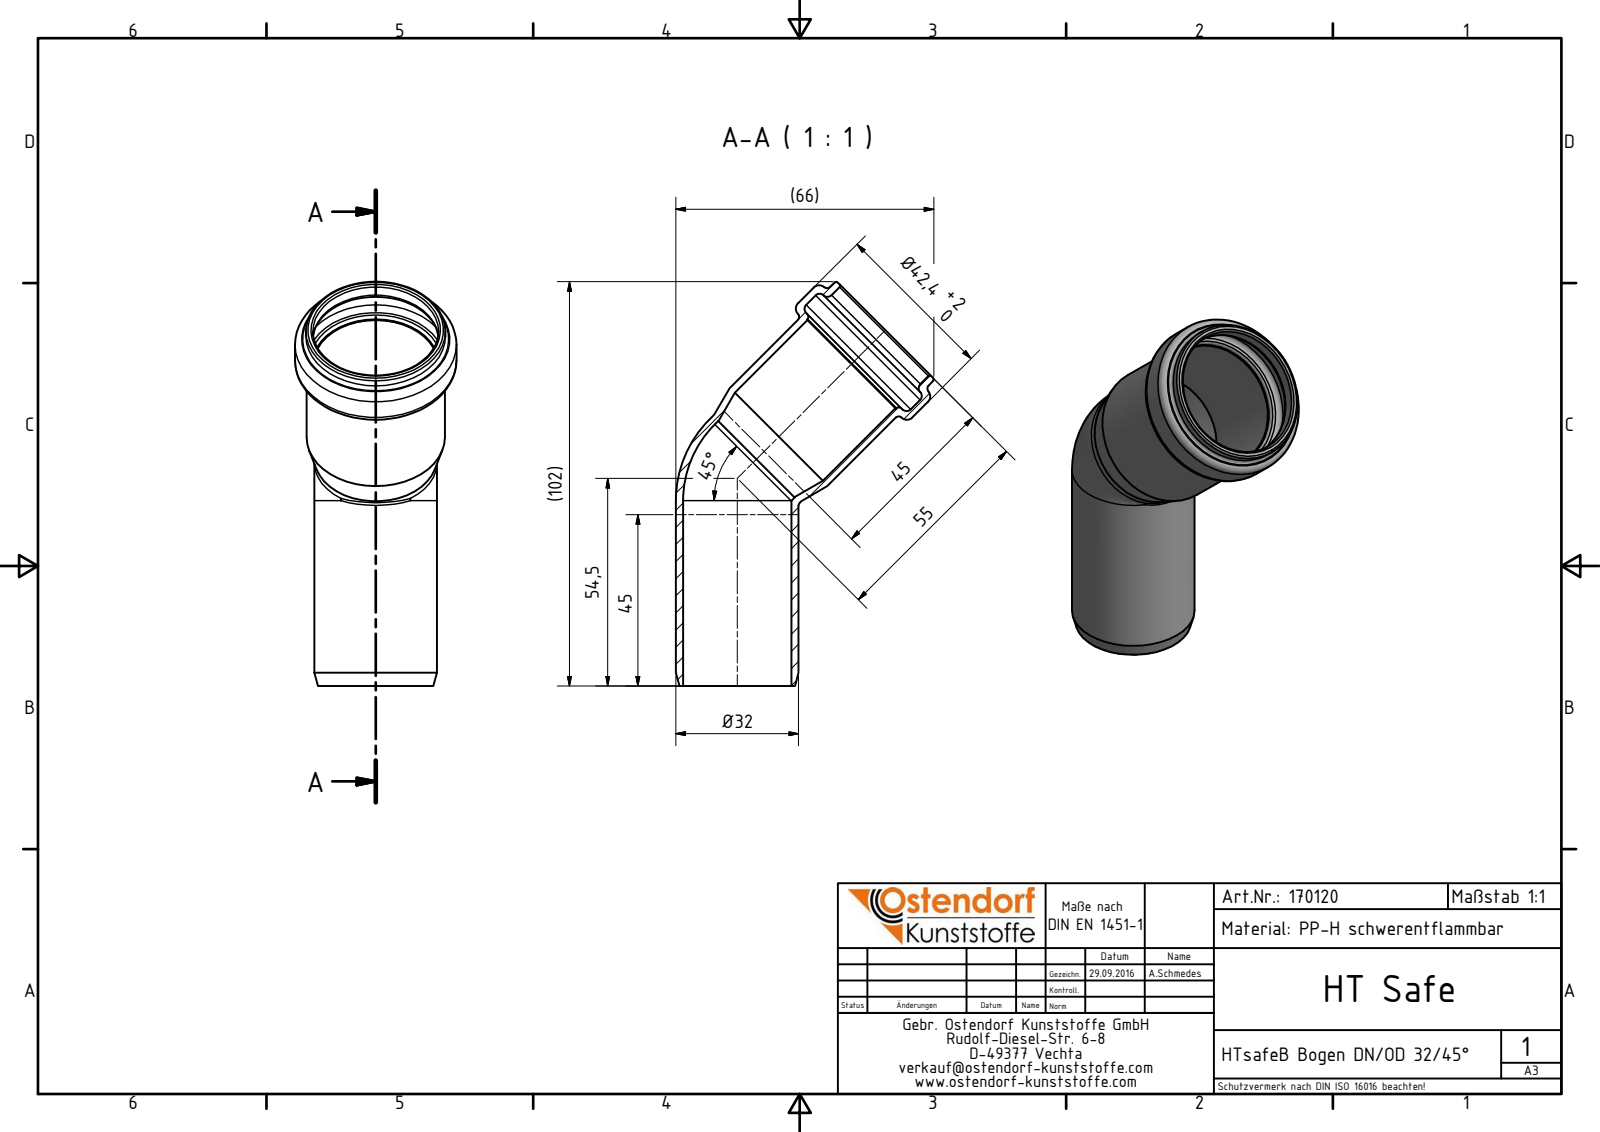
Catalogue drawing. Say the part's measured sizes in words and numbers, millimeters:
The part is named "170120 HTsafeB DN_OD 32_45°". Its 3-D file was written by "Autodesk Inventor 2016 (AUTOMOTIVE_DESIGN)". It is 1 solid with 35 faces: 4 planar, 11 cylindrical and 20 other. Overall it measures 106.12 by 67.72 by 42.4 millimeters. Its volume is 21 124 cubic millimeters and its surface area 23 323 square millimeters. Round holes: 2 of diameter 28.43, 1 of diameter 32.7, 1 of diameter 33, 1 of diameter 38.8. Round bosses or shafts: 2 of diameter 32.2, 1 of diameter 42.4, 1 of diameter 36.6, 1 of diameter 36.3. The main face-to-face distances are 12.62, 35.27, 47.89.
